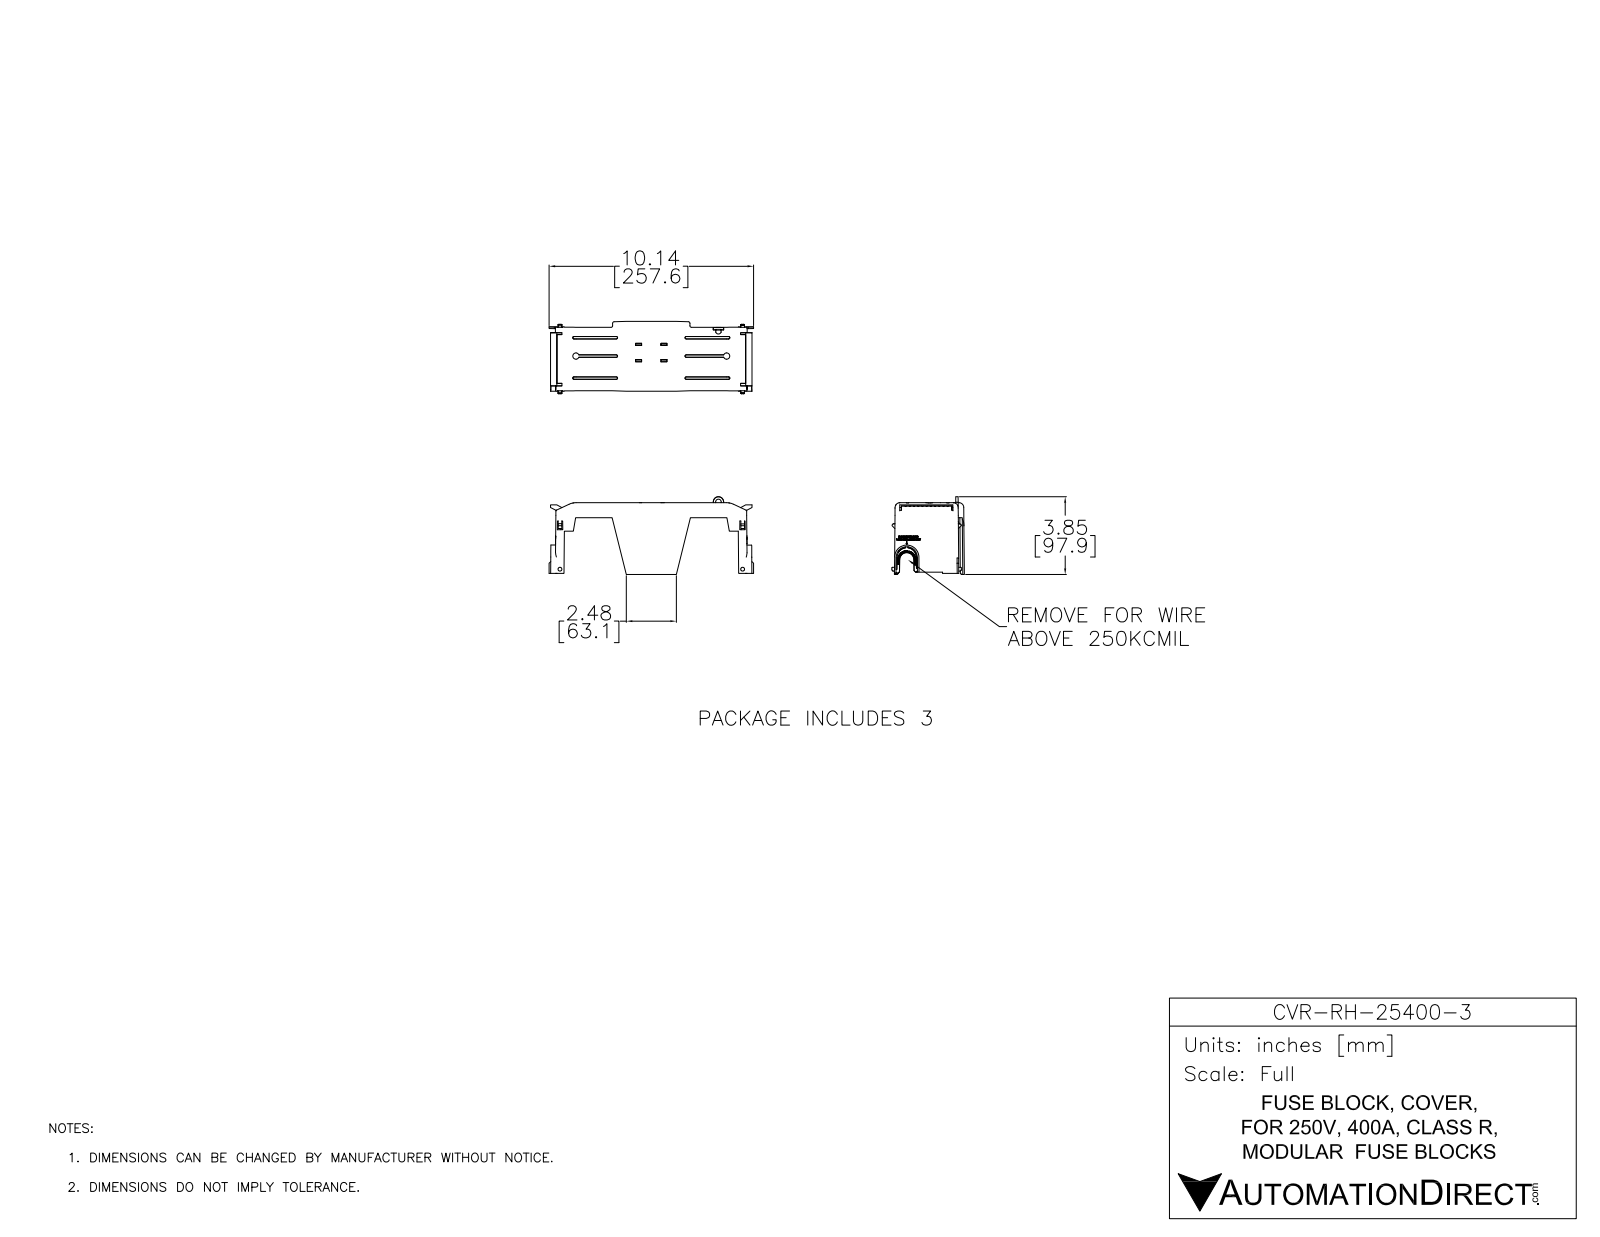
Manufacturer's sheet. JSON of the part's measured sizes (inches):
{"part_name": "CVR-RH-25400-3", "step_written_by": "SolidWorks 2017 (AUTOMOTIVE_DESIGN)", "units": "inches", "bodies": {"solids": 1, "faces": 2380, "planar": 1598, "cylindrical": 106, "other": 676}, "overall_size": [10.143, 3.853, 3.593], "volume_in3": 7.778, "surface_area_in2": 207.6, "round_holes": [[0.276, 1]], "partial_cylinders_radius": [[0.039, 19], [0.118, 8], [0.157, 7], [0.236, 7], [0.079, 6], [0.01, 2], [0.02, 2], [0.232, 2]], "face_to_face_distances": [0.079, 0.276, 0.197, 0.354, 0.118, 0.669, 0.392, 1.338, 0.24, 1.098]}
